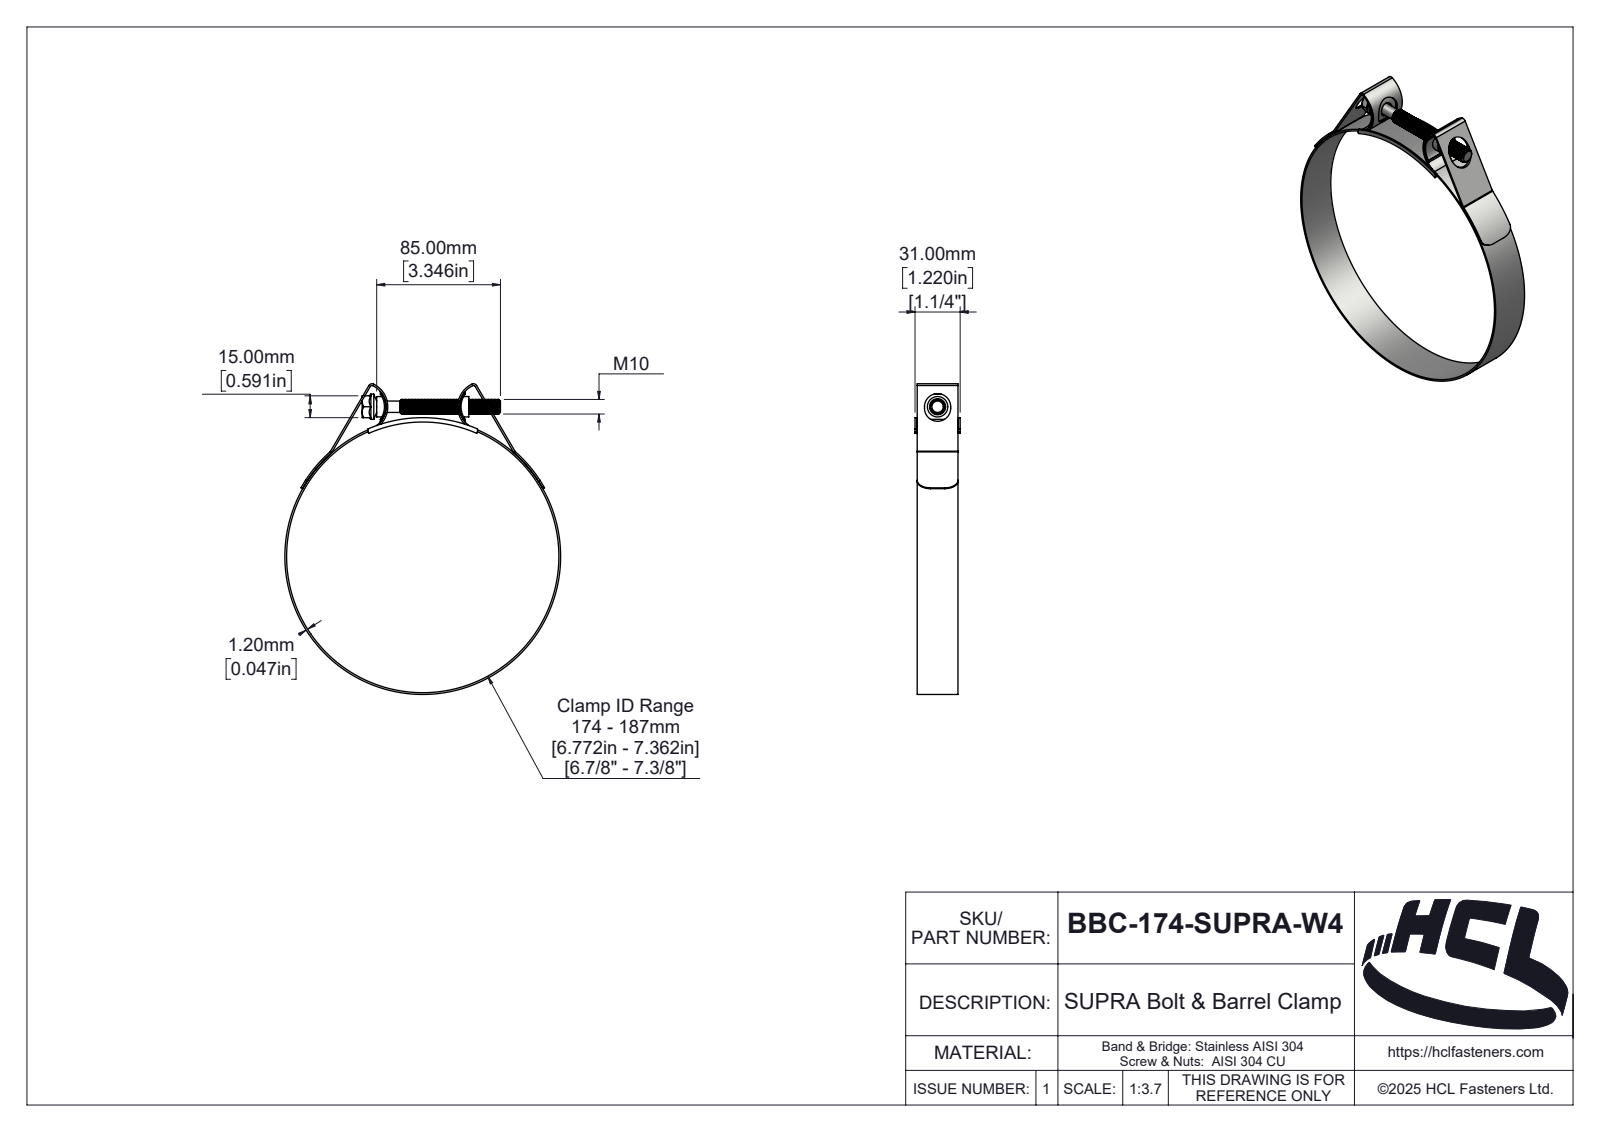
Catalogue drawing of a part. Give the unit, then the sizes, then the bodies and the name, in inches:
Units: inches
Overall size (bounding box): 8.397 × 7.457 × 1.22
Round holes (diameter × count): ⌀7.362 ×1
Round bosses / shafts (diameter × count): ⌀7.457 ×1, ⌀0.682 ×1, ⌀0.551 ×1, ⌀0.394 ×1, ⌀0.307 ×1
Partial cylindrical surfaces — rounded edges, fillets, slot ends (radius × count): R0.039 ×4, R0.051 ×2, R0.079 ×2, R0.098 ×2, R0.126 ×2, R0.354 ×2, R0.589 ×2, R0.629 ×2
Main face-to-face distances: 0.047, 1.102, 0.059, 1.161, 1.173, 1.114, 1.22, 1.126, 0.591, 0.098
Volume: 2.249 in³ · Surface area: 86.9 in²
Bodies: 5 solids, 384 faces (50 planar, 247 cylindrical, 87 other)
Part name (STEP PRODUCT): BBC-174-SUPRA-W4
STEP written by: SolidWorks 2025 (AUTOMOTIVE_DESIGN)
